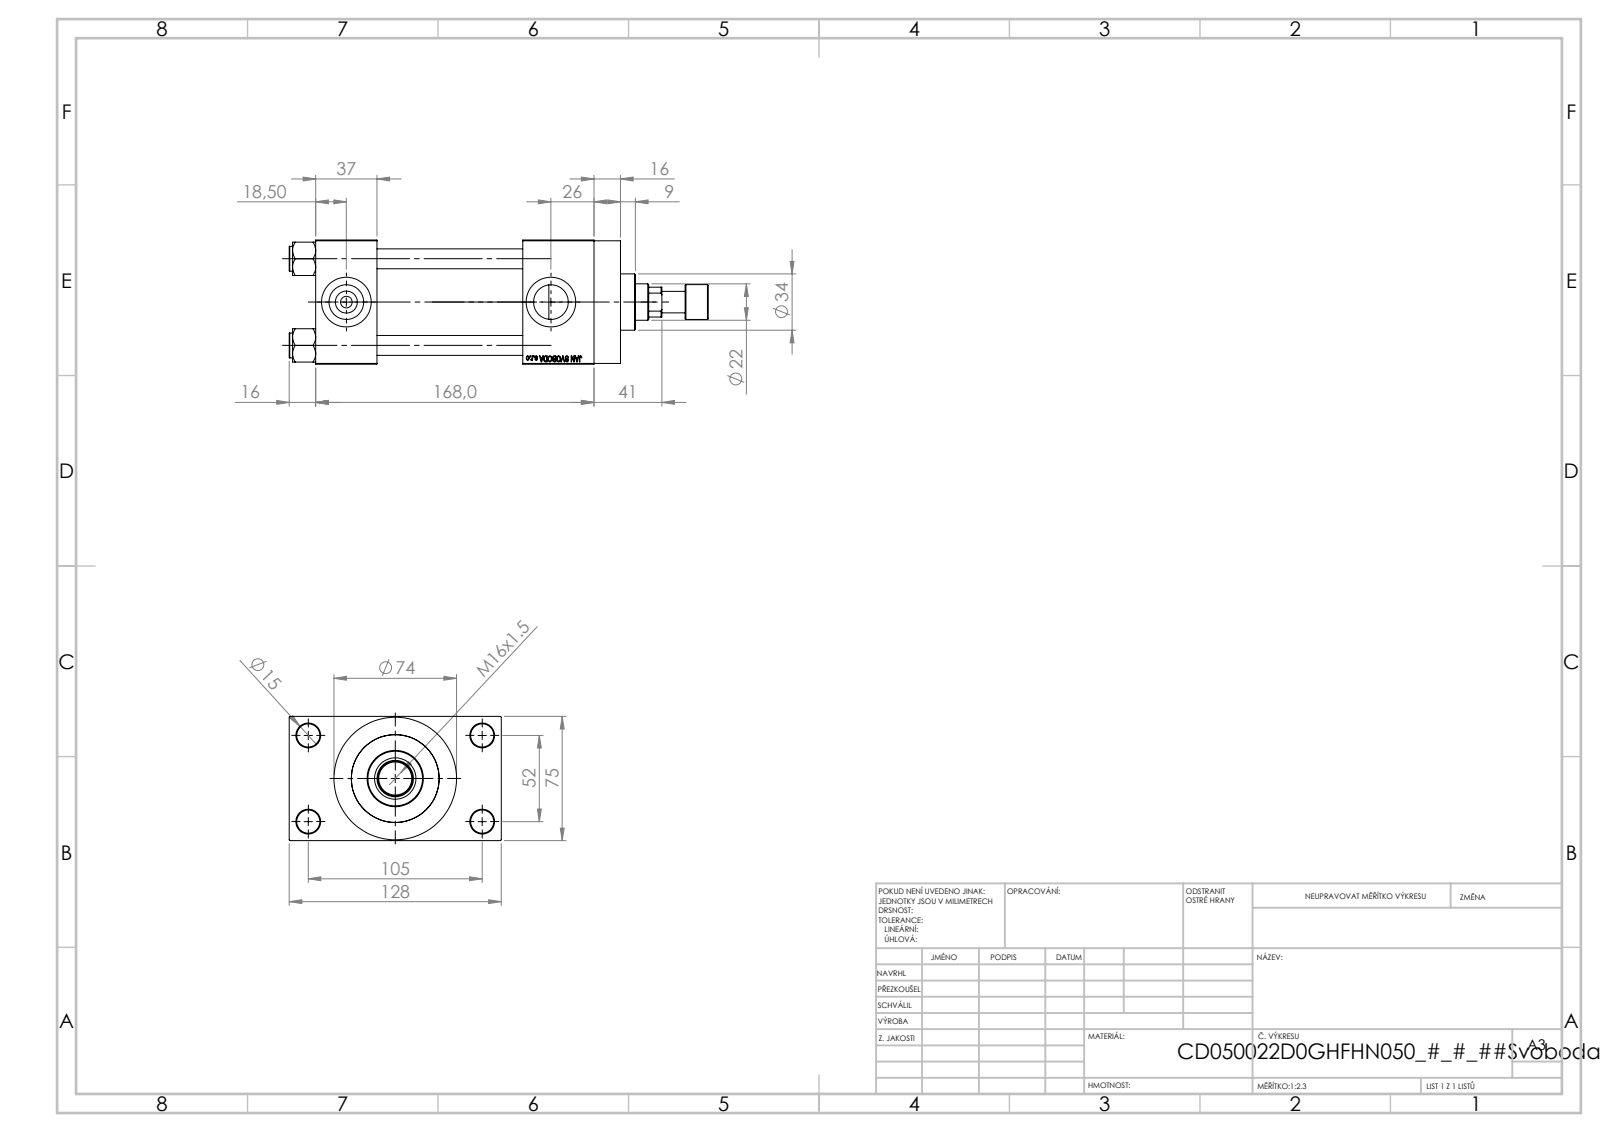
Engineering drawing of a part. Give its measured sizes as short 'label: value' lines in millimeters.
name: V215CD_VCP_D; V215CD_NUT_M5_D; V215CD_VC_A; V215CR_ROD_END_F (+2 more)
written by: SolidWorks 2019 (CONFIG_CONTROL_DESIGN)
unit: mm
bodies: 12 solids, 1114 faces (500 planar, 92 cylindrical, 522 other)
size: 253 × 128 × 75
volume: 844 179 mm³; area: 185 434 mm²
holes: 4× ⌀12, 4× ⌀14, 2× ⌀7, 2× ⌀20.96, 2× ⌀30, 1× ⌀10.5, 1× ⌀22, 1× ⌀25, 1× ⌀41, 1× ⌀50, 1× ⌀53
bosses: 4× ⌀15, 1× ⌀74, 1× ⌀56, 1× ⌀34, 1× ⌀21, 1× ⌀13
face distances: 75, 88, 125, 37, 26.5, 168, 131, 43, 101.5, 16
hole spacings: 26.35, 36.98, 52.3, 58.43, 58.59, 78.65, 94.37, 52
